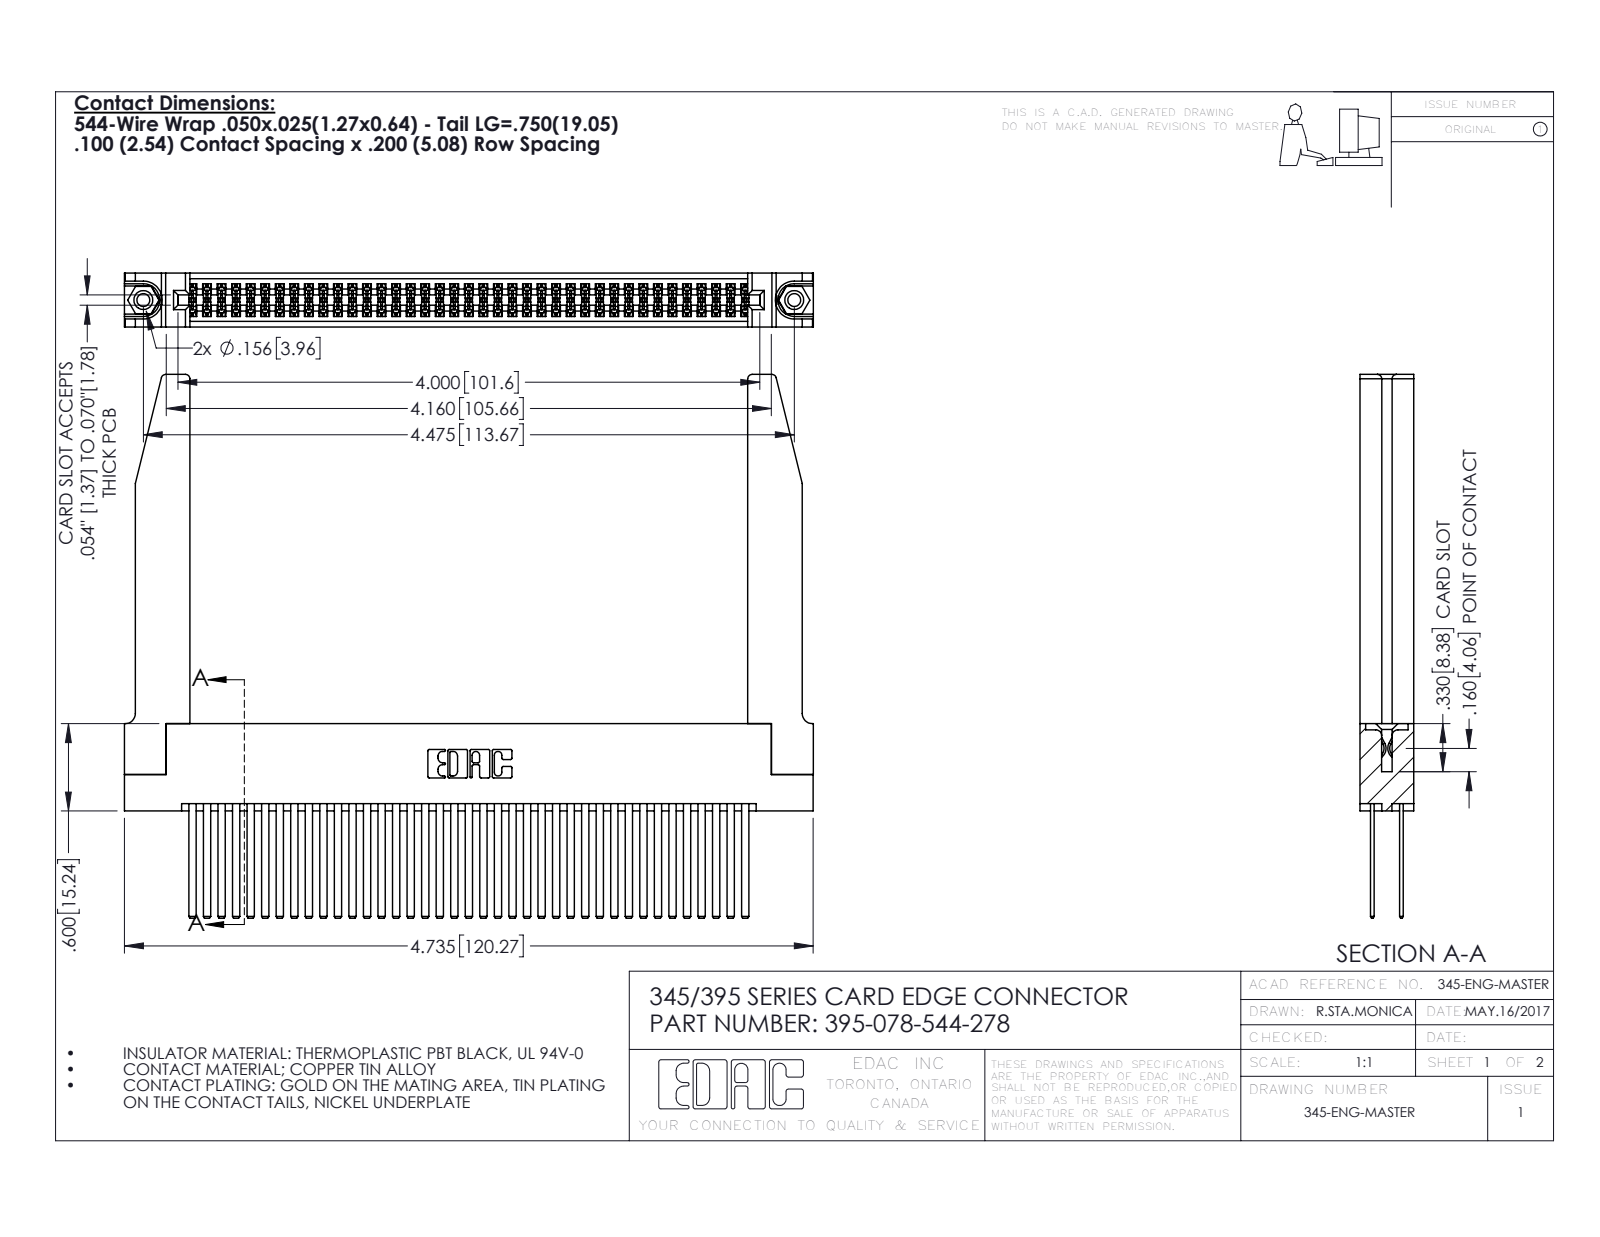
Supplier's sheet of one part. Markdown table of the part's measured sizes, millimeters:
| quantity | value |
| --- | --- |
| part name | 345-250-001_345-250-001-102; 345 Part_Flush Mounting Lugs - 0.156 Dia-TH; 345-220-078_345-220-078; 395-078-544-278 (+1 more) |
| STEP written by | SolidWorks 2016 (CONFIG_CONTROL_DESIGN) |
| units | millimeters |
| bodies | 83 solids, 3792 faces (2484 planar, 1256 cylindrical, 52 other) |
| overall size | 120.3 × 94.9 × 9.4 |
| volume | 20 520 mm³ |
| surface area | 28 830 mm² |
| round holes (diameter × count) | 2.3 × 2, 3.2 × 2, 4 × 2, 1.6 × 1 |
| round bosses / shafts (diameter × count) | 3.9 × 2 |
| partial cylindrical surfaces (radius × count) | 0.2 × 117, 0.3 × 22, 0.8 × 8, 0.2 × 6, 0.8 × 6, 0.7 × 3, 0.4 × 2, 0.5 × 2 |
| main face-to-face distances | 1.8, 7.6, 5.1, 2.5, 6.9, 0.6, 9.4, 5.7, 4.4, 3.8 |
| hole center spacings | 6.9, 107.7, 113.7 |
